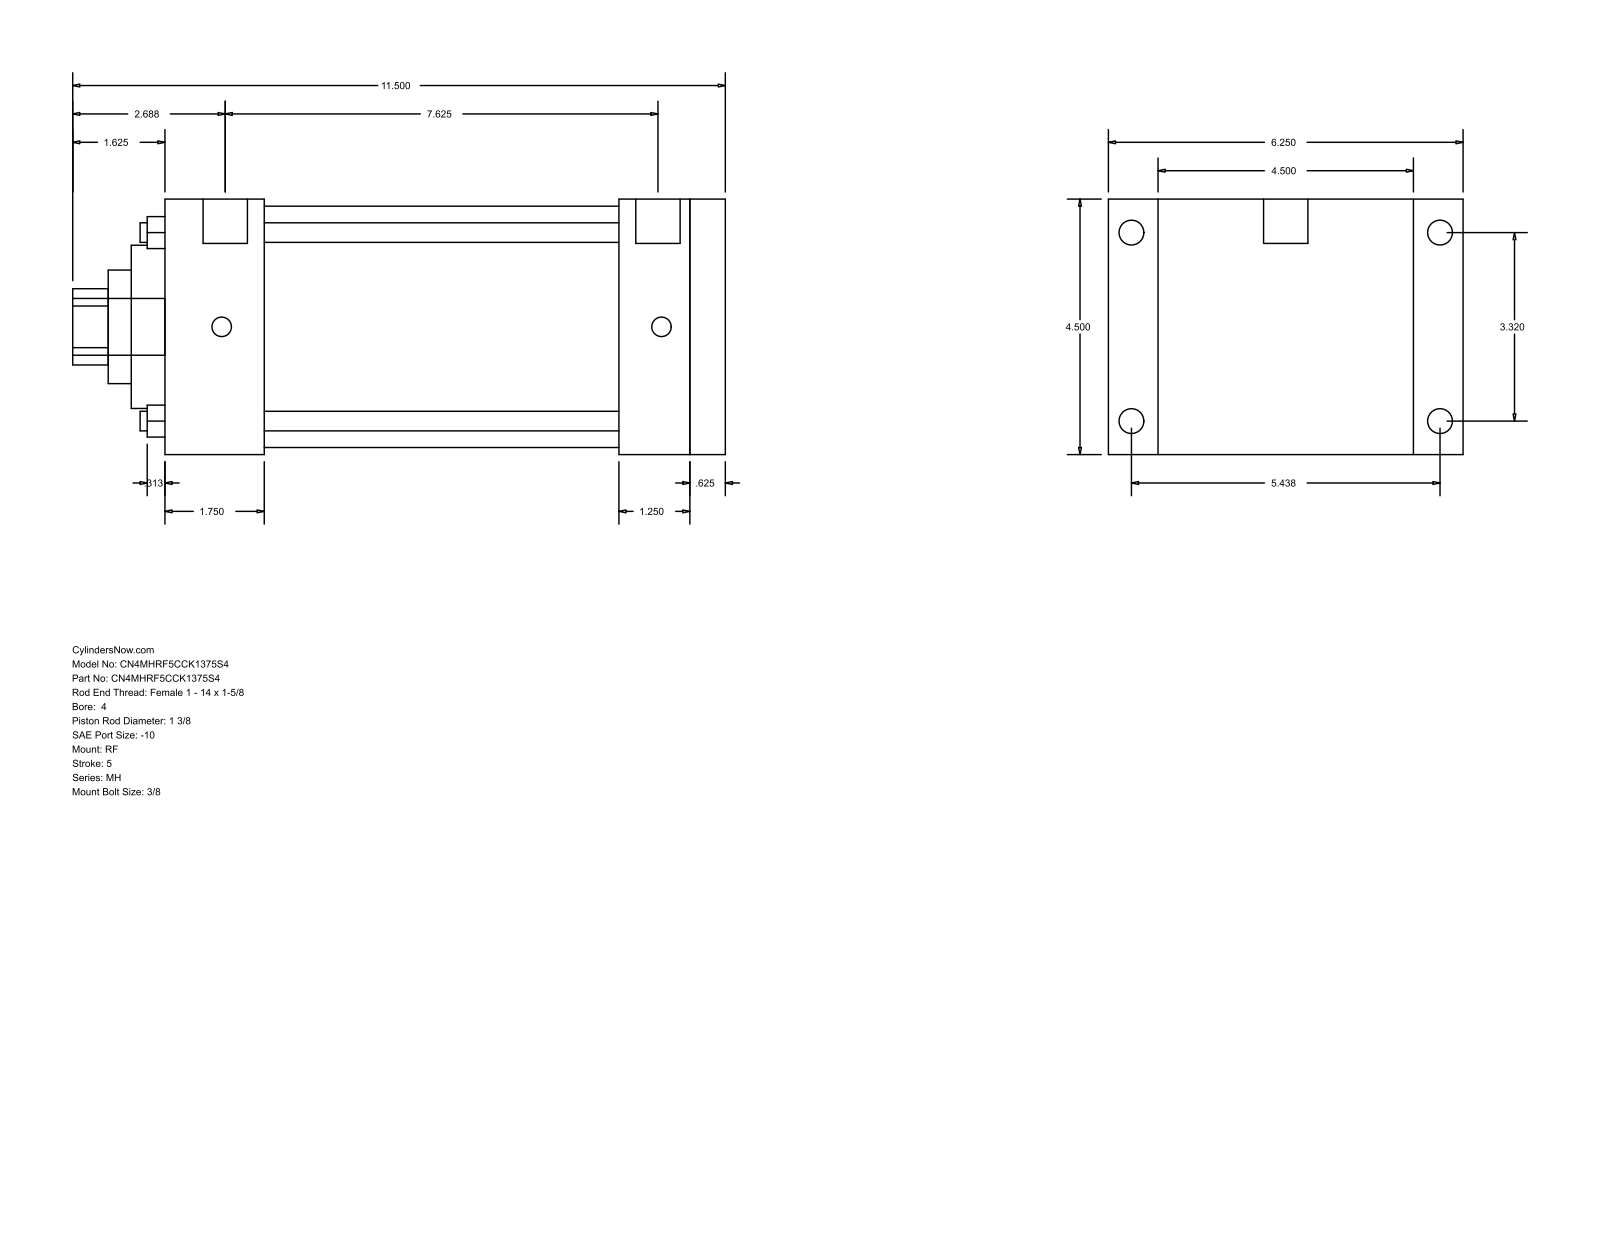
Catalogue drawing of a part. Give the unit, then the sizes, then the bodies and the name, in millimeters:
Units: millimetres
Overall size (bounding box): 292.1 × 158.75 × 114.3
Round holes (diameter × count): ⌀8.76 ×4, ⌀34.92 ×1, ⌀50.8 ×1, ⌀73.03 ×1, ⌀107.95 ×1
Round bosses / shafts (diameter × count): ⌀11.13 ×4, ⌀8.73 ×4, ⌀19.84 ×2, ⌀25.4 ×1
Partial cylindrical surfaces — rounded edges, fillets, slot ends (radius × count): R17.06 ×1
Main face-to-face distances: 114.3, 250.83, 234.96, 15.87, 44.45, 190.51, 206.38, 203.2, 158.75, 31.76
Hole centre spacings: 59.62, 84.32, 119.25
Bodies: 0 solids, 94 faces (65 planar, 29 cylindrical, 0 other)
Part name (STEP PRODUCT): MH_RF__0400_1.375
STEP written by: GSSL Pune (CONFIG_CONTROL_DESIGN)
